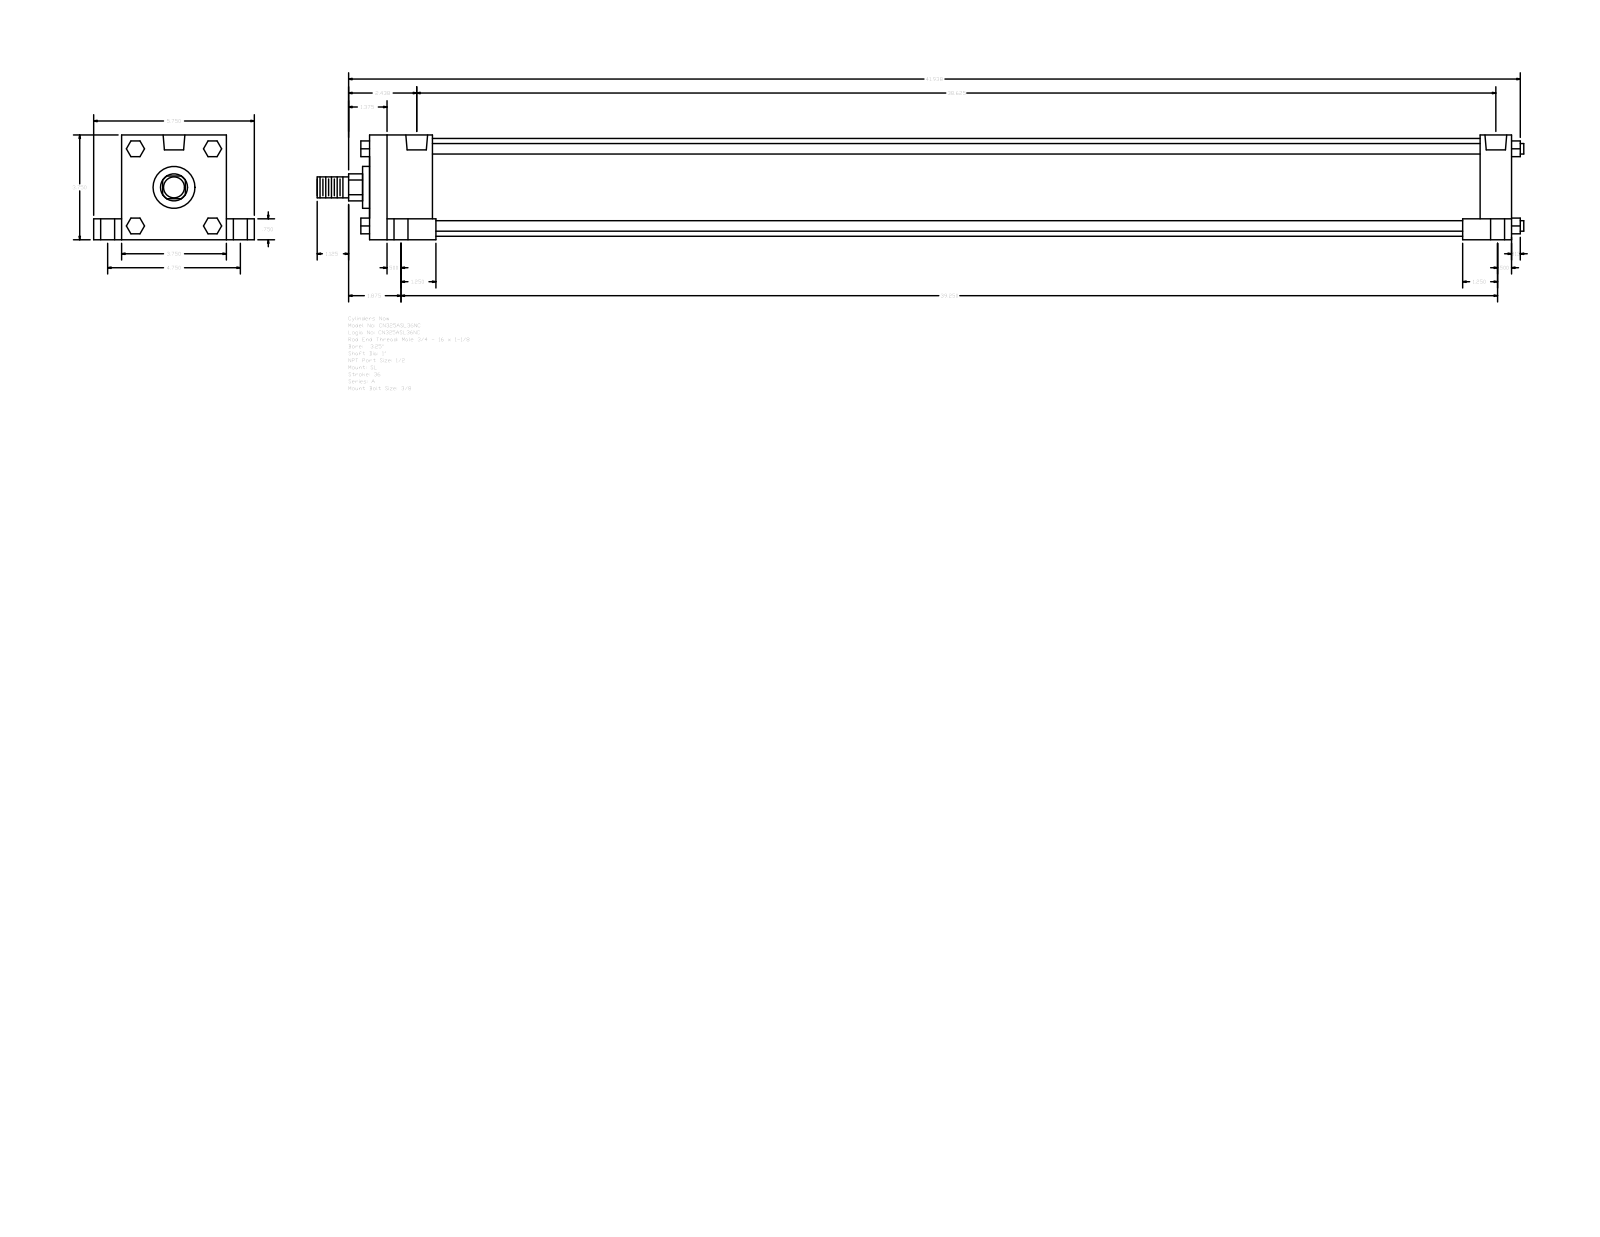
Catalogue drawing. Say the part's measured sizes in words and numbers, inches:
The part is named "A_SL__0325_1". Its 3-D file was written by "GSSL Pune (CONFIG_CONTROL_DESIGN)". It is 0 solids with 150 faces: 114 planar, 36 cylindrical and 0 other. Overall it measures 43.187 by 5.75 by 3.75 inches. Round holes: 4 of diameter 0.344, 4 of diameter 0.5, 4 of diameter 0.75, 2 of diameter 0.778. Round bosses or shafts: 4 of diameter 0.375, 1 of diameter 3.5, 1 of diameter 1.5, 1 of diameter 1, 1 of diameter 0.75. Partial cylindrical surfaces (rounded edges, fillets, slot ends): 1 of radius 0.484. The main face-to-face distances are 3.75, 40.875, 0.75, 1, 4.75, 3, 2.25, 39.75, 37.5, 38.625. The hole center spacings are 0.125, 2.376, 2.383, 2.441, 2.473, 4.75, 38.375, 38.5.
